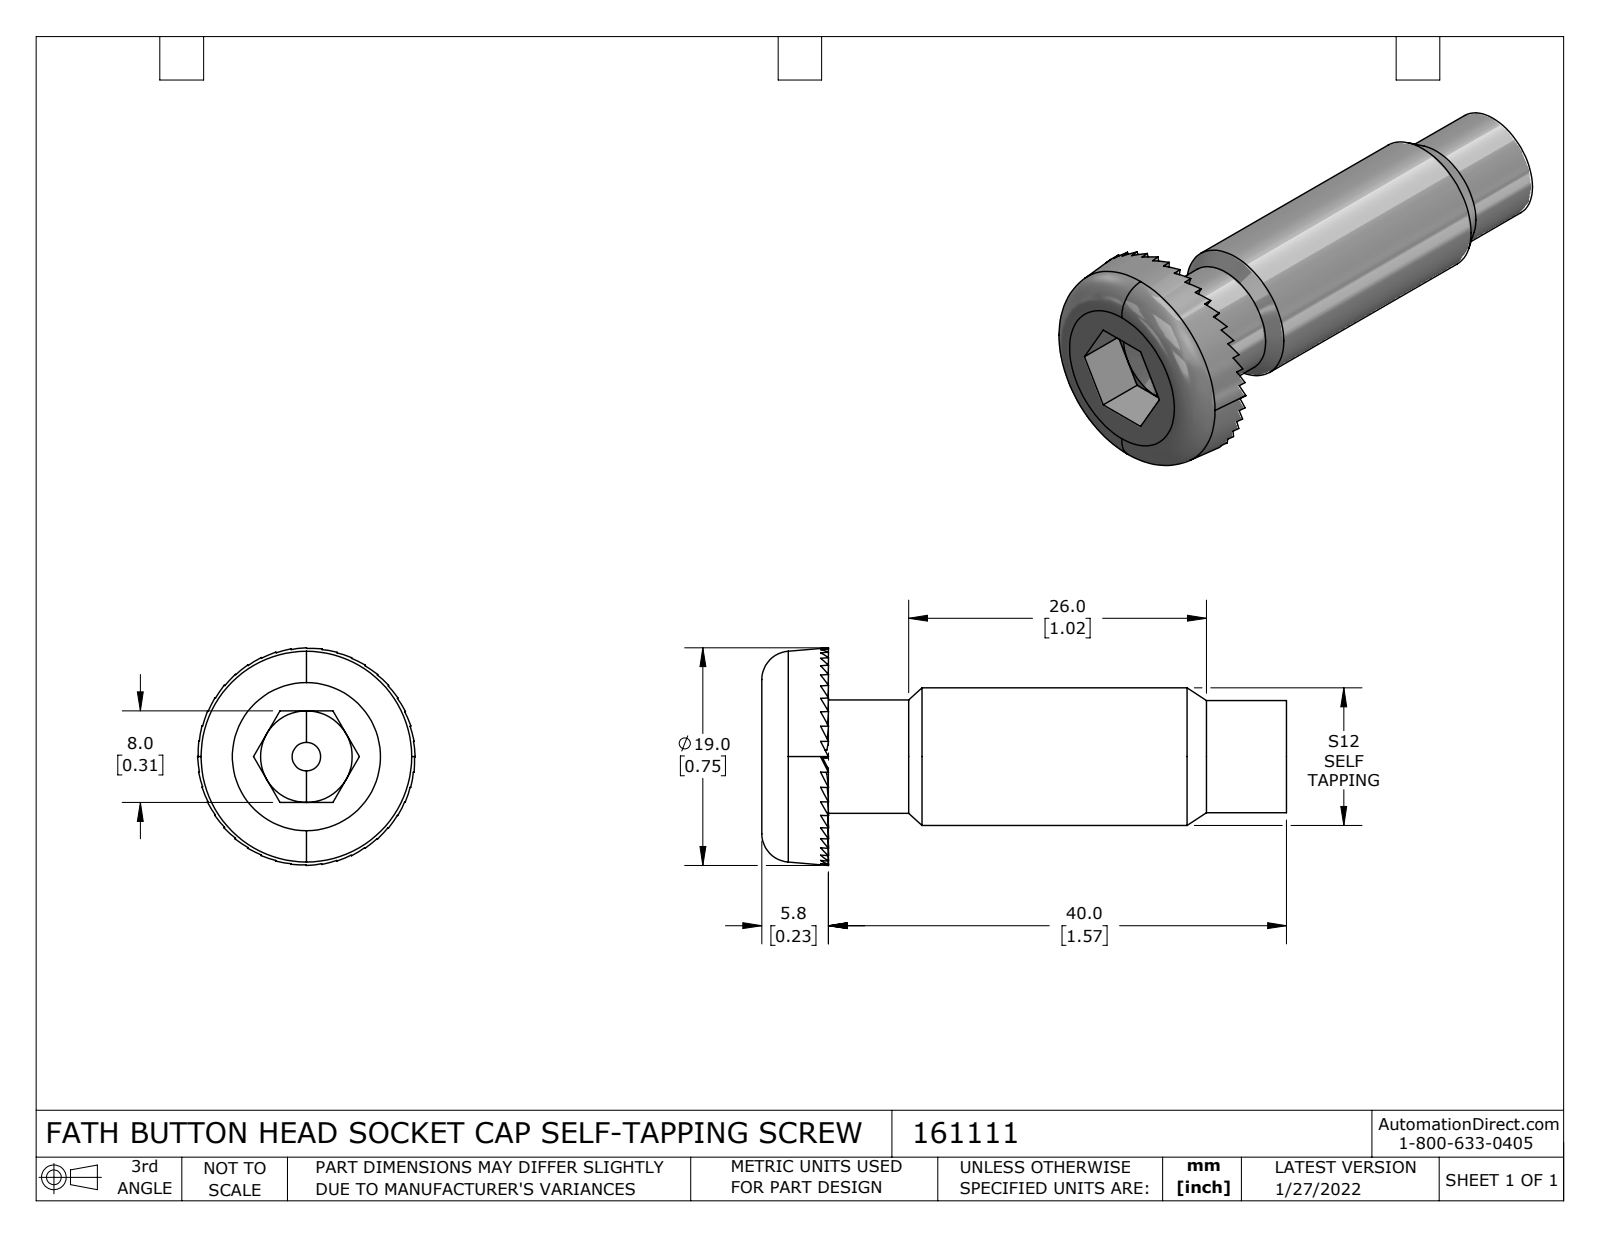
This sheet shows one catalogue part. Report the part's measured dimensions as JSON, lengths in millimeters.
{"part_name": "161111", "step_written_by": "SolidWorks 2021 (CONFIG_CONTROL_DESIGN)", "units": "millimeters", "bodies": {"solids": 1, "faces": 119, "planar": 103, "cylindrical": 6, "other": 10}, "overall_size": [45.81, 19, 19], "volume_mm3": 5118, "surface_area_mm2": 2490, "round_bosses_or_shafts": [[12, 1], [9.9, 1], [9.8, 1]], "face_to_face_distances": [45.8, 8, 0.52, 41.6, 4.2, 40.01, 1.59, 5.79, 0.54]}
